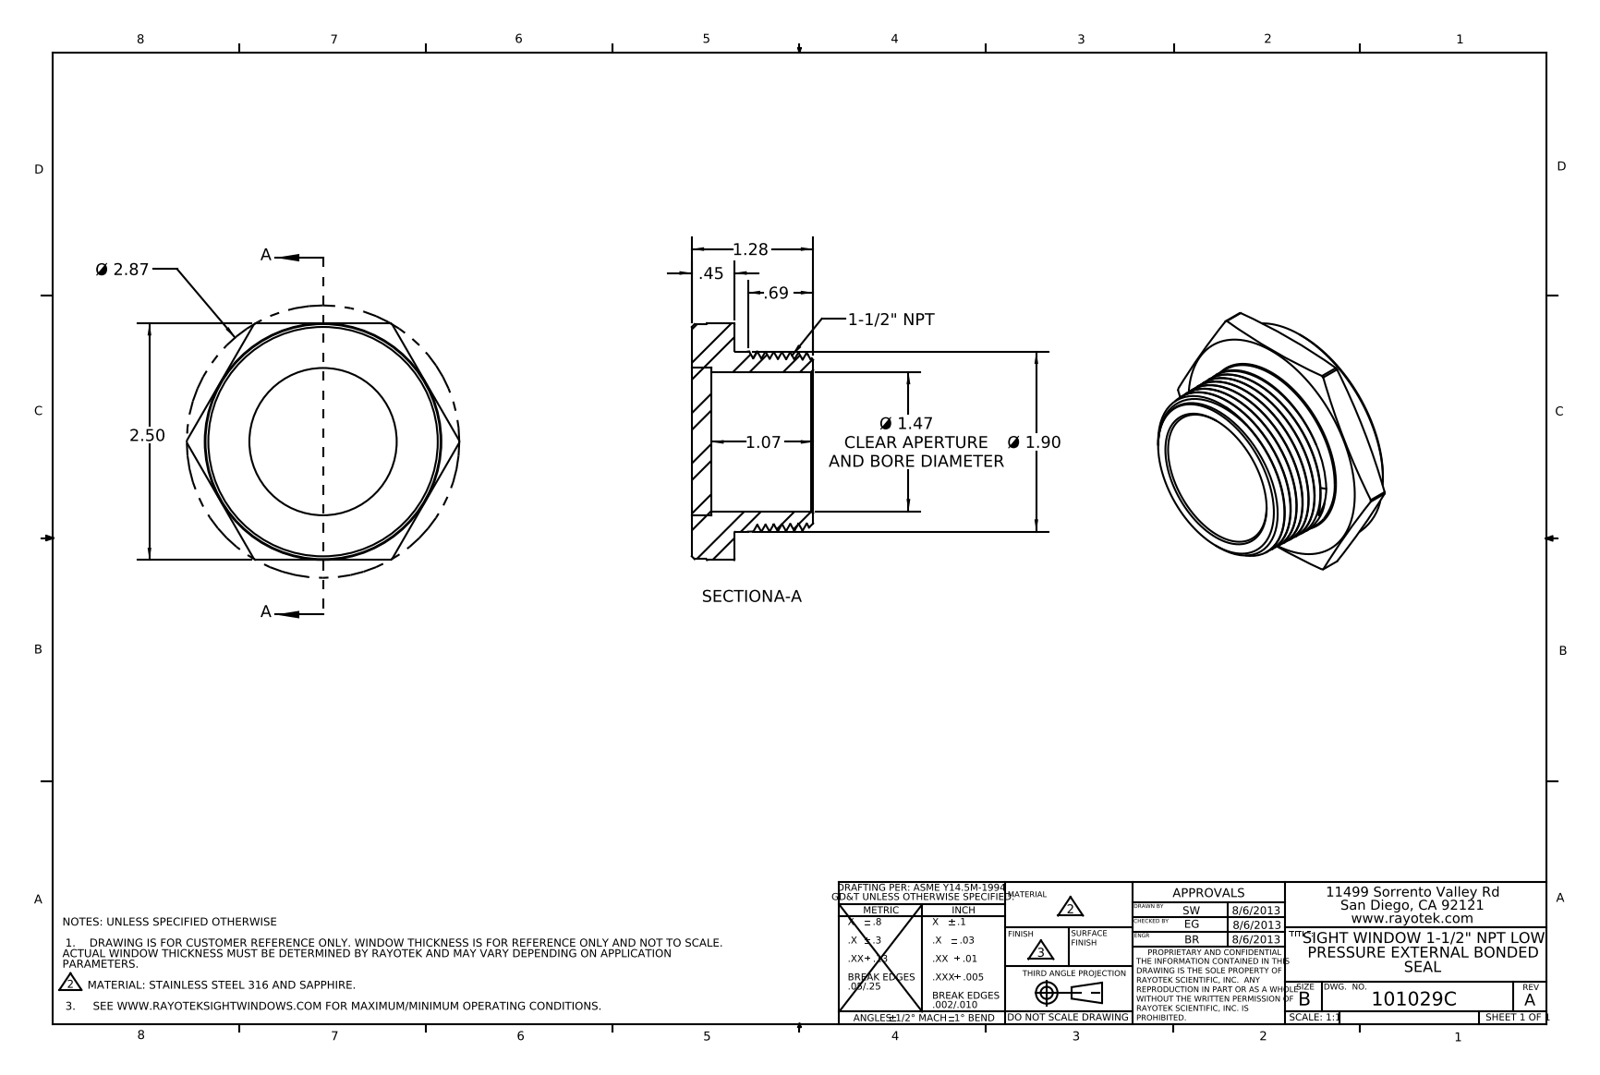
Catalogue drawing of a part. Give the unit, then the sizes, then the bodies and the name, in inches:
Units: inches
Overall size (bounding box): 2.875 × 2.5 × 1.28
Round holes (diameter × count): ⌀1.47 ×1, ⌀1.554 ×1
Round bosses / shafts (diameter × count): ⌀2.48 ×1, ⌀1.9 ×1
Partial cylindrical surfaces — rounded edges, fillets, slot ends (radius × count): R1.437 ×1
Main face-to-face distances: 0.207, 0.45, 0.243, 2.5, 1.28, 1.073, 0.83
Volume: 2.688 in³ · Surface area: 29.03 in²
Bodies: 2 solids, 65 faces (15 planar, 17 cylindrical, 33 other)
Part name (STEP PRODUCT): 403029
STEP written by: SolidWorks 2012 (AUTOMOTIVE_DESIGN)
